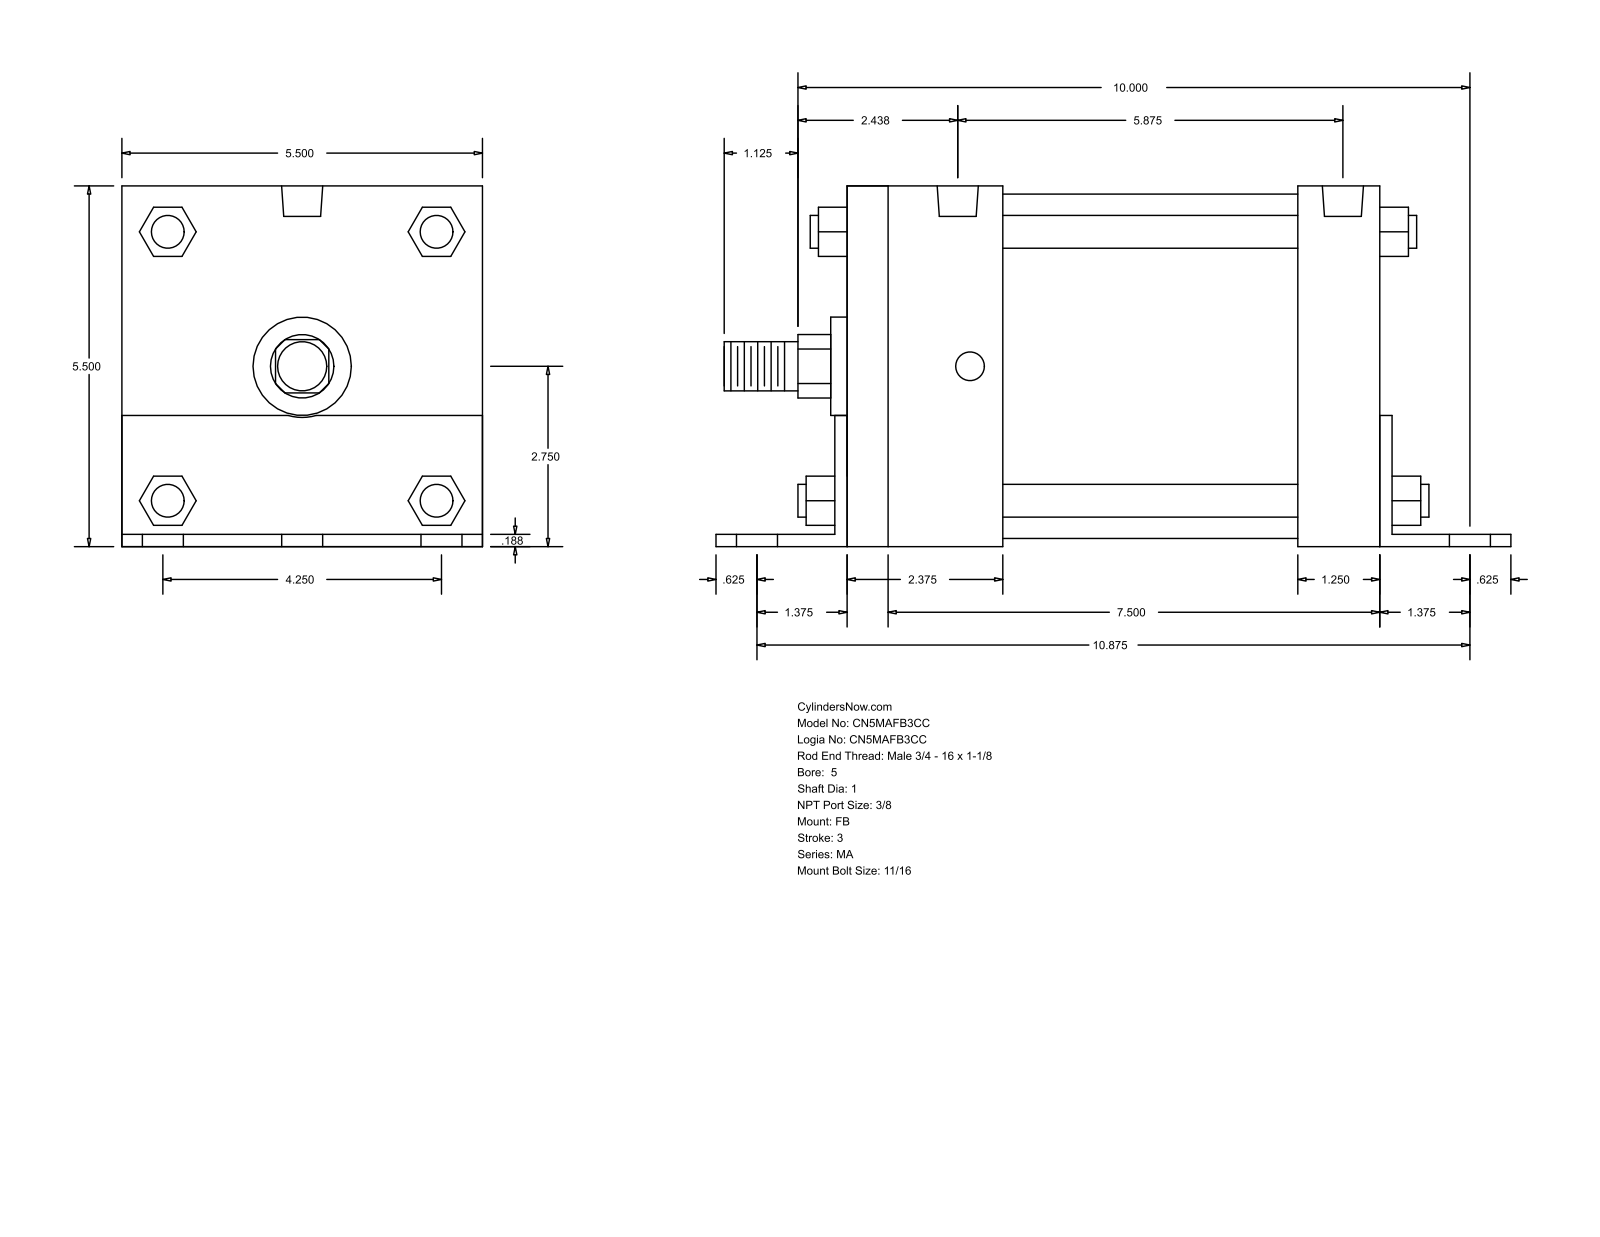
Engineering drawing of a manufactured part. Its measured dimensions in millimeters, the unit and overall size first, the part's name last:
Units: millimetres
Overall size (bounding box): 307.98 × 139.75 × 139.7
Round holes (diameter × count): ⌀17.46 ×6, ⌀11.11 ×4, ⌀15.93 ×2
Round bosses / shafts (diameter × count): ⌀12.7 ×4, ⌀133.35 ×1, ⌀38.1 ×1, ⌀25.4 ×1, ⌀19.05 ×1
Partial cylindrical surfaces — rounded edges, fillets, slot ends (radius × count): R12.29 ×1, R19.81 ×1
Main face-to-face distances: 139.7, 4.76, 139.75, 211.14, 4.71, 134.99, 206.38, 215.9, 36.51, 31.75
Hole centre spacings: 53.98, 281.45, 276.23, 4.76, 73.04, 76.33, 94.68, 98.63
Bodies: 0 solids, 140 faces (105 planar, 35 cylindrical, 0 other)
Part name (STEP PRODUCT): MA_FB__0500_1
STEP written by: GSSL Pune (CONFIG_CONTROL_DESIGN)
